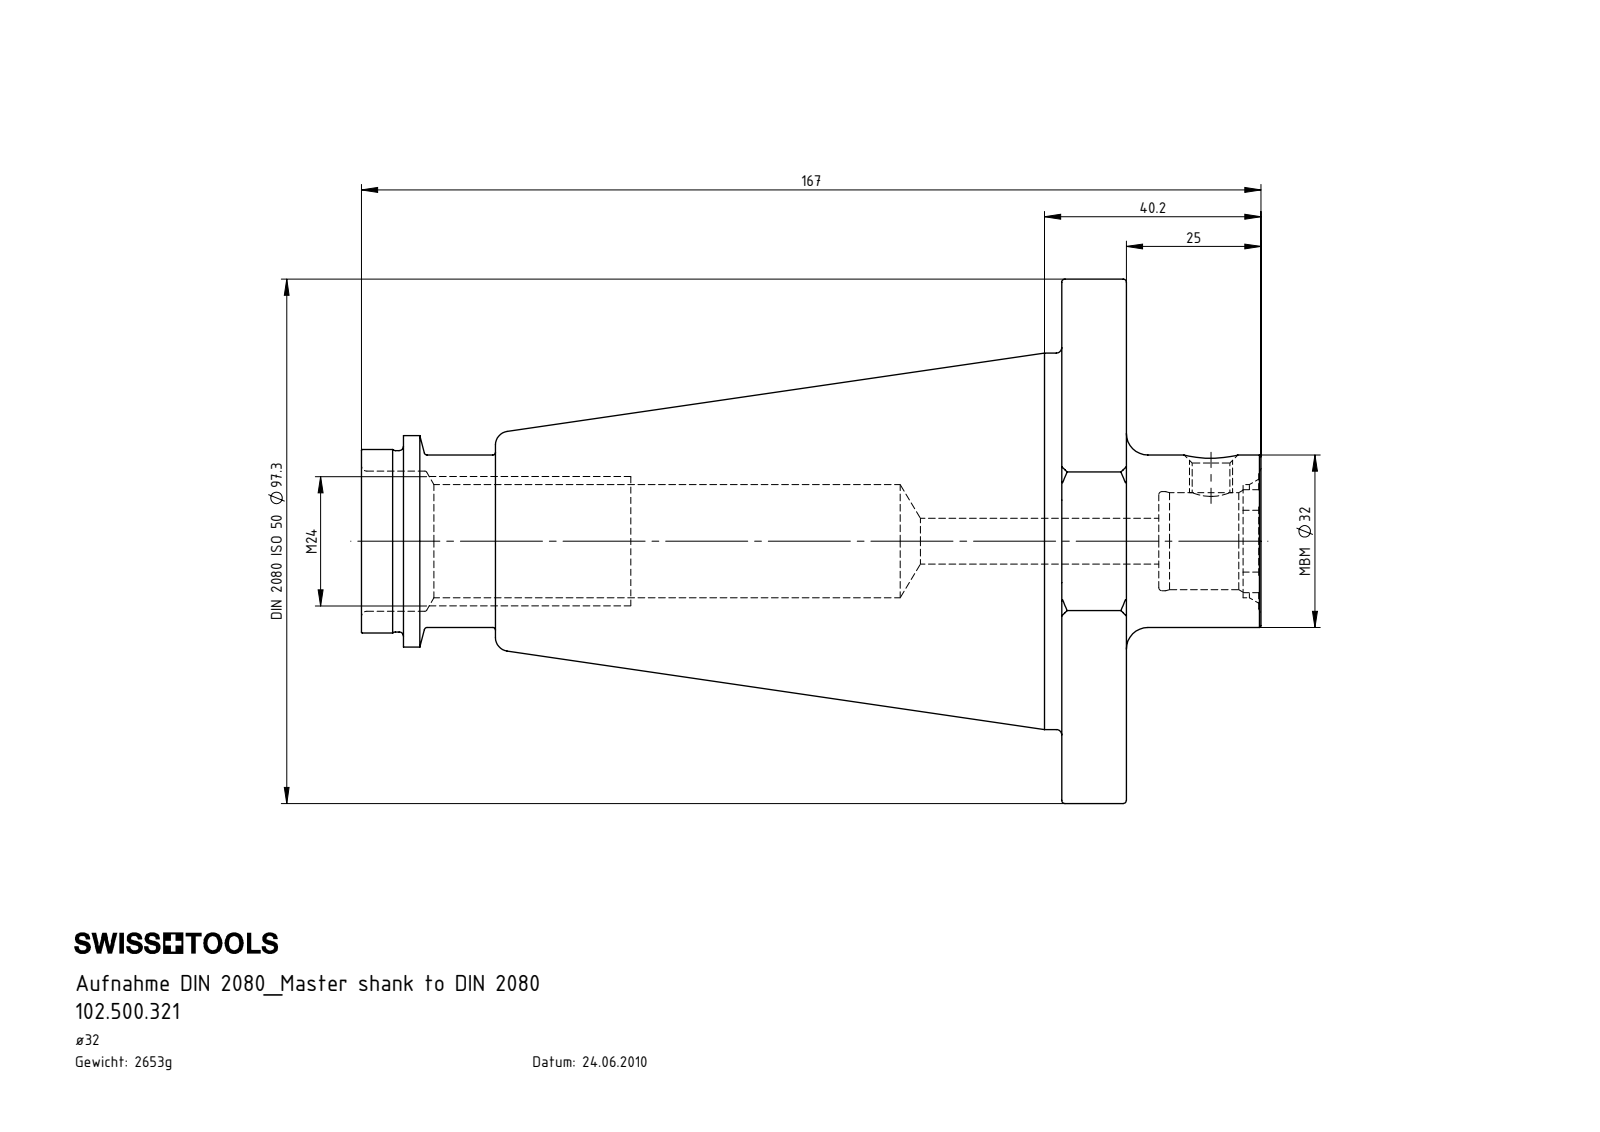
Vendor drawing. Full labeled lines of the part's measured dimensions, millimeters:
Part name (STEP PRODUCT): 102.500.321
STEP written by: SolidWorks 2017 (CONFIG_CONTROL_DESIGN)
Units: millimetres
Bodies: 1 solid, 130 faces (33 planar, 49 cylindrical, 48 other)
Overall size (bounding box): 167 × 97.3 × 93.84
Volume: 337 983 mm³ · Surface area: 47 883 mm²
Round holes (diameter × count): ⌀7 ×1, ⌀8.5 ×1, ⌀18 ×1, ⌀18.4 ×1, ⌀21 ×1, ⌀26 ×1
Round bosses / shafts (diameter × count): ⌀97.3 ×1, ⌀69.85 ×1, ⌀39.24 ×1, ⌀34.05 ×1, ⌀33.65 ×1, ⌀32 ×1
Partial cylindrical surfaces — rounded edges, fillets, slot ends (radius × count): R2 ×12, R3.2 ×4, R12.18 ×1
Main face-to-face distances: 12, 130, 142, 70.2, 7.8, 122.2, 134.2, 167, 159.2, 37
